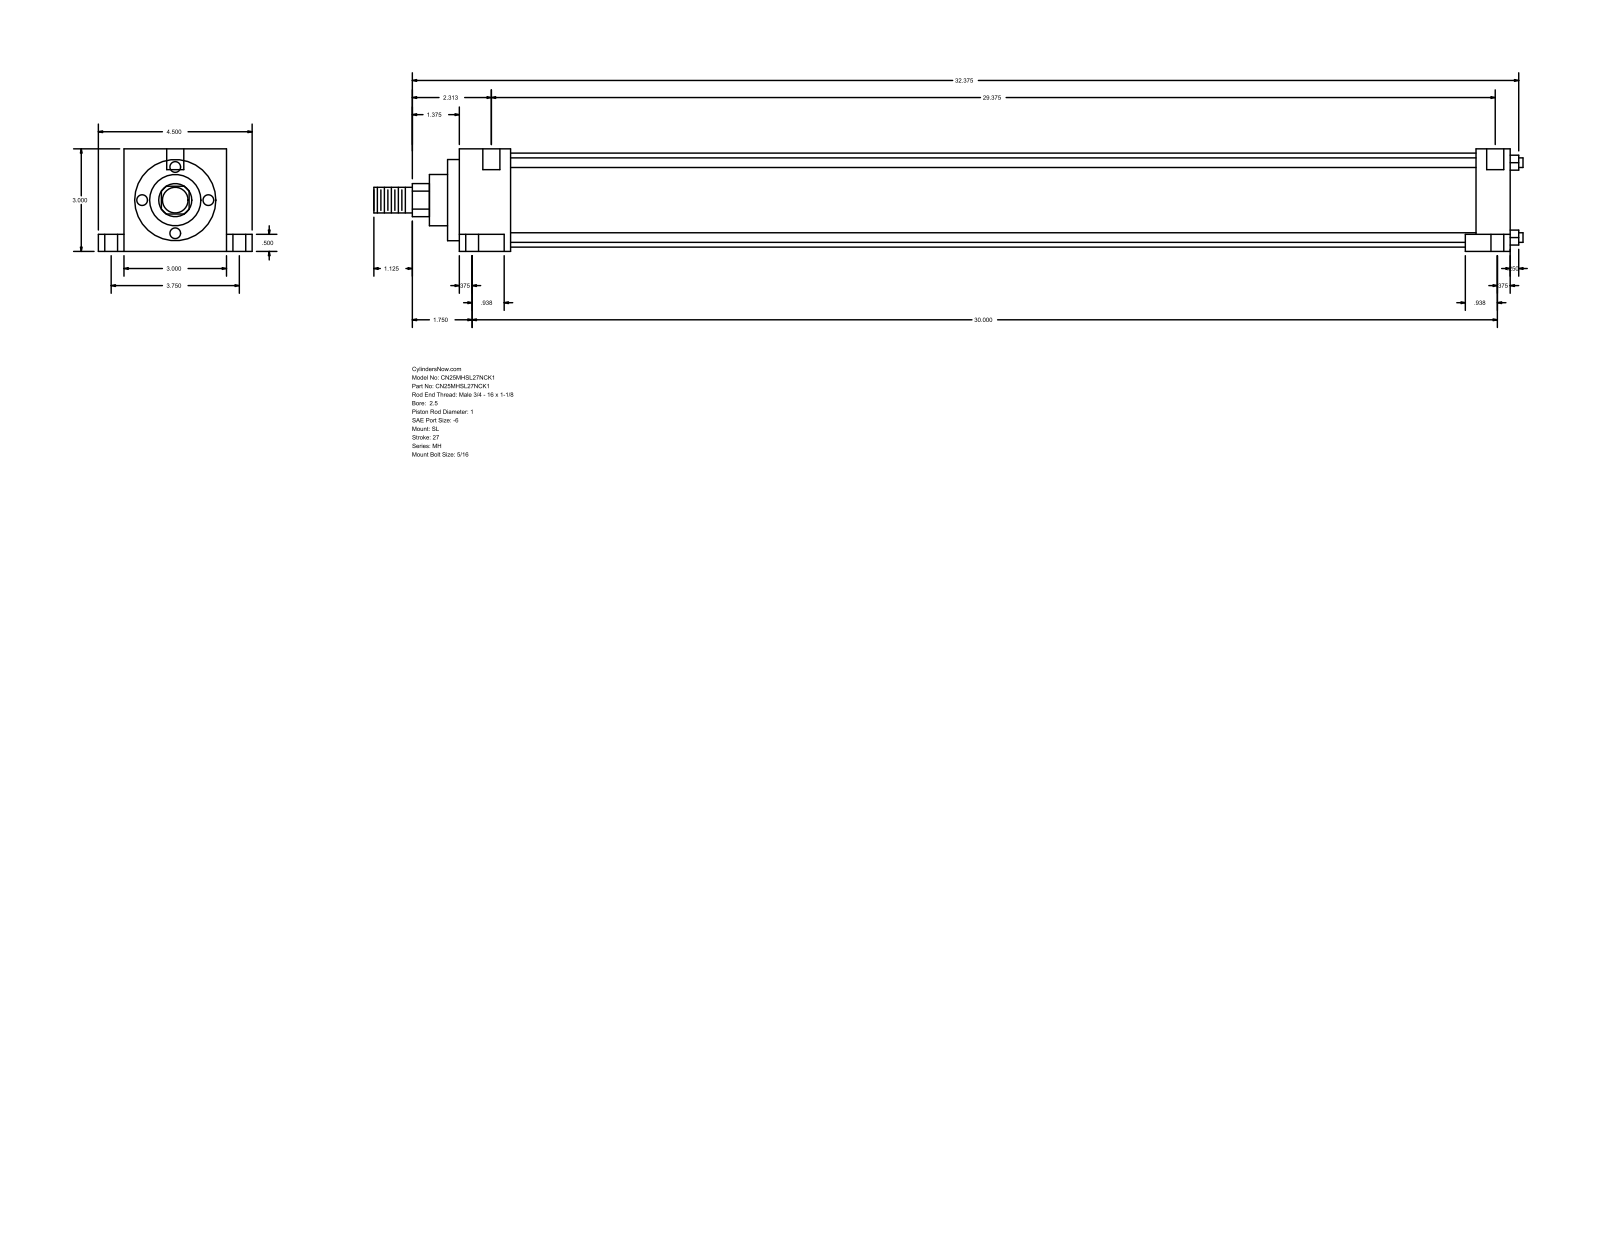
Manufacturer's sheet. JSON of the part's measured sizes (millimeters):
{"part_name": "MH_SL__0250_1", "step_written_by": "GSSL Pune (CONFIG_CONTROL_DESIGN)", "units": "millimeters", "bodies": {"solids": 0, "faces": 86, "planar": 61, "cylindrical": 25, "other": 0}, "overall_size": [854.08, 114.3, 76.2], "round_holes": [[5.56, 2], [9.53, 2], [15.88, 2], [12.7, 1]], "round_bosses_or_shafts": [[7.14, 4], [69.85, 1], [60.33, 1], [38.1, 1], [25.4, 1], [19.05, 1]], "partial_cylinders_radius": [[12.29, 1]], "face_to_face_distances": [76.2, 25.4, 764.39, 789.79, 12.7, 63.5, 19.05, 95.25, 13.49, 777.88], "hole_center_spacings": [47.65, 3.18, 95.24]}
